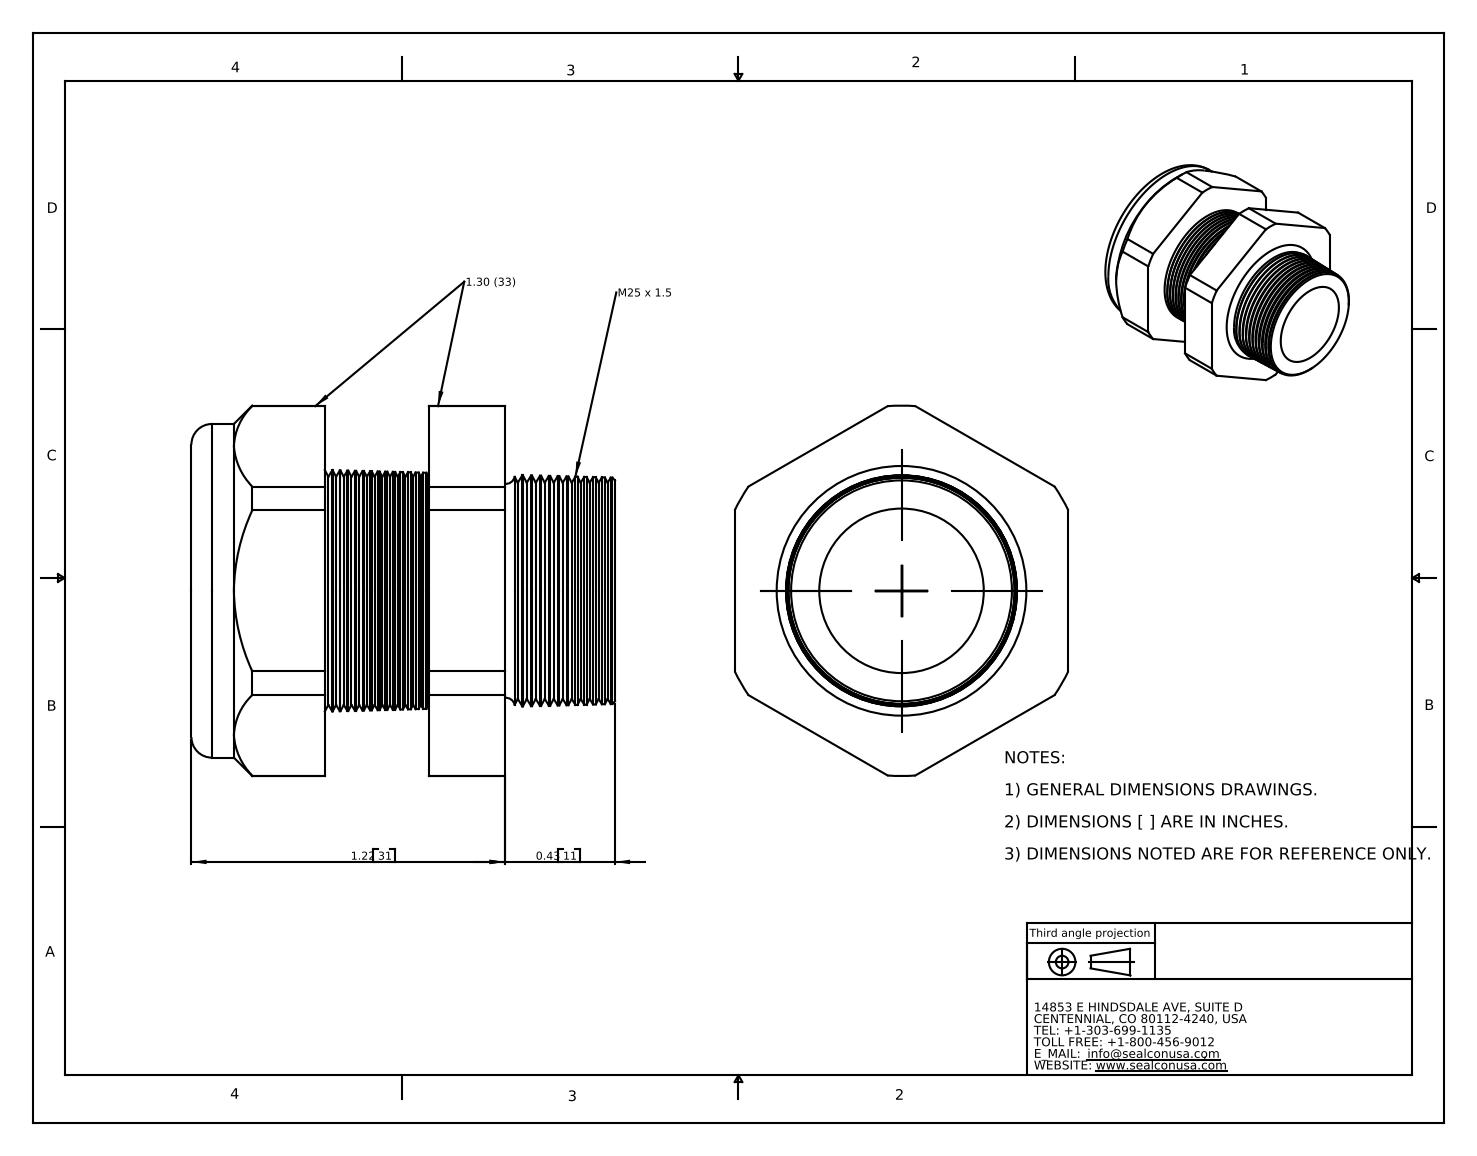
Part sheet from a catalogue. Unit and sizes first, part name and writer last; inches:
Units: inches
Overall size (bounding box): 1.65 × 1.443 × 1.3
Round holes (diameter × count): ⌀0.69 ×1, ⌀0.71 ×1
Round bosses / shafts (diameter × count): ⌀1.3 ×1
Partial cylindrical surfaces — rounded edges, fillets, slot ends (radius × count): R0.721 ×1
Main face-to-face distances: 1.3, 0.405, 0.7, 0.295, 0.52, 0.925, 1.22, 0.35, 0.17, 0.575
Volume: 1.191 in³ · Surface area: 16.55 in²
Bodies: 2 solids, 206 faces (20 planar, 20 cylindrical, 166 other)
Part name (STEP PRODUCT): CD25MP-GY
STEP written by: SolidWorks 2007 (CONFIG_CONTROL_DESIGN)
